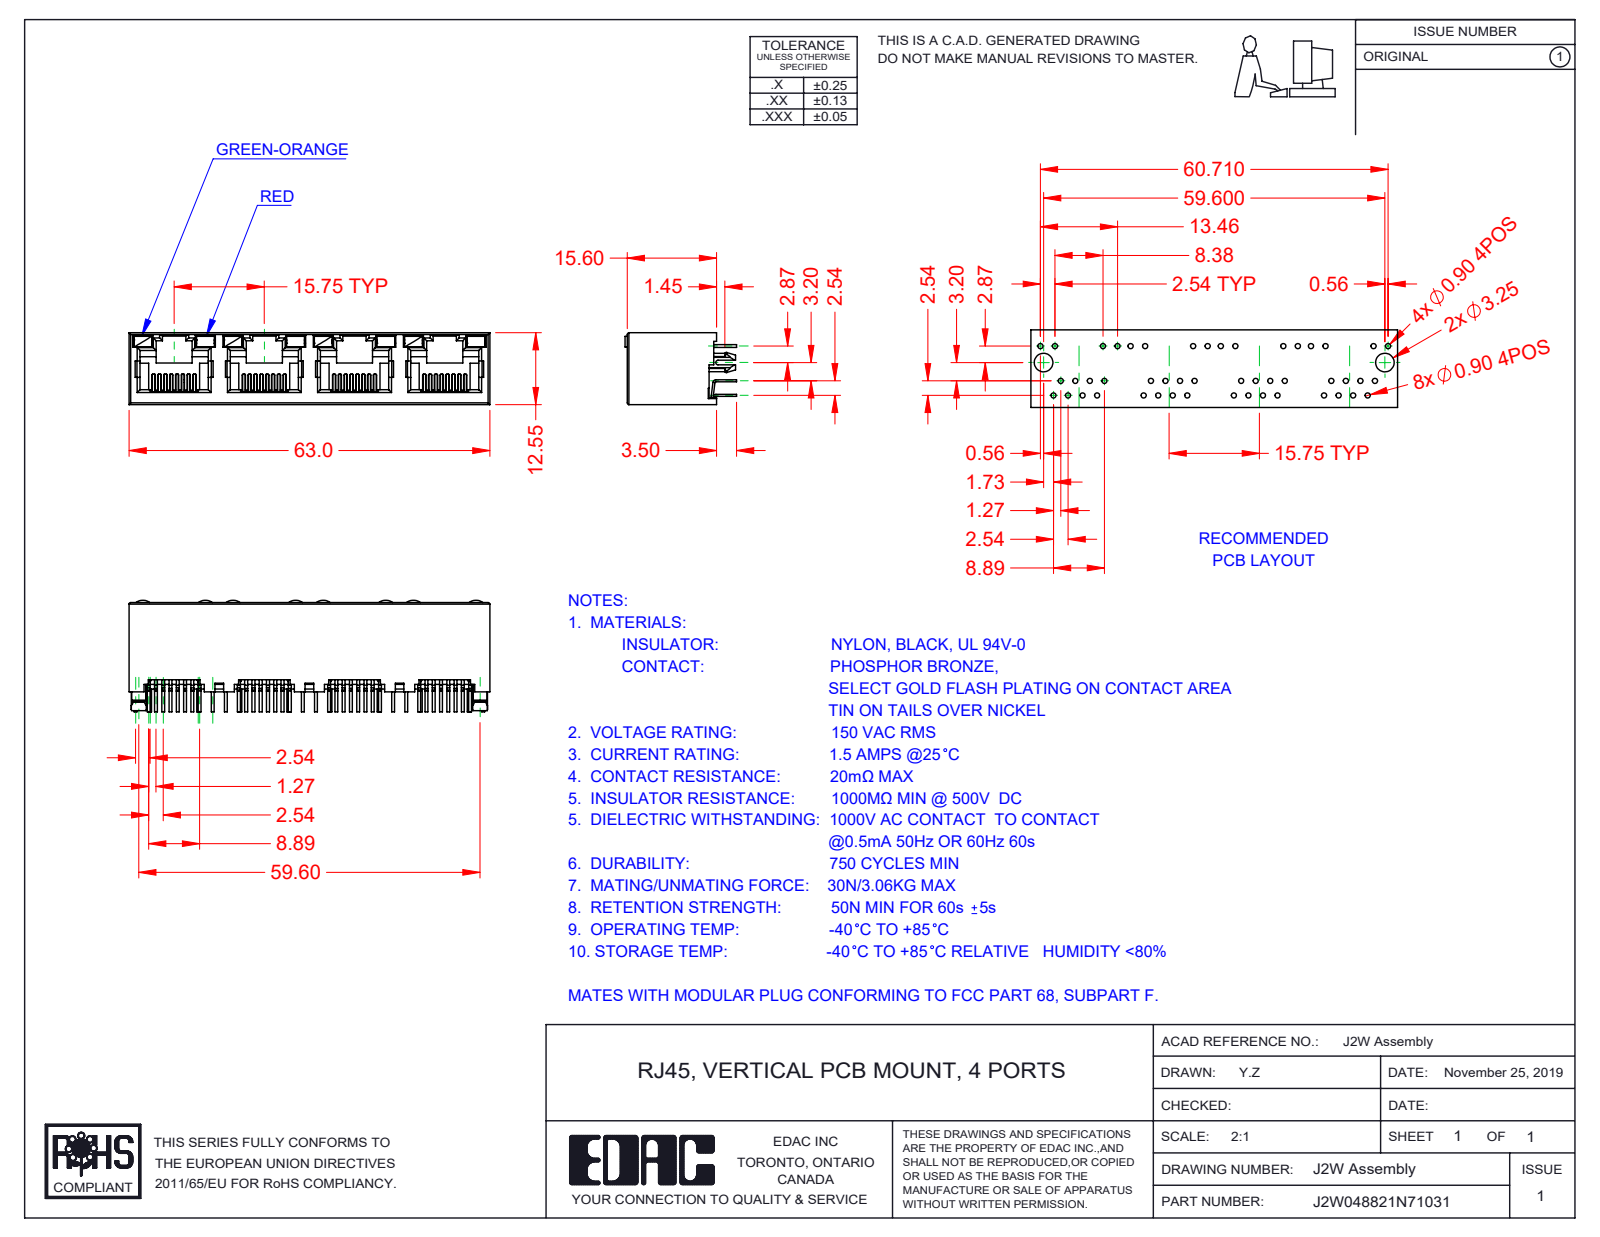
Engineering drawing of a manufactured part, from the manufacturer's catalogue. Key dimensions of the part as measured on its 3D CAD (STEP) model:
Part name (STEP PRODUCT): 2W LED RH_2-Red; 2W LED LH_7-Green-Orange; J2W048821N72131; 2W Contacts (+2 more)
STEP written by: SolidWorks 2016 (CONFIG_CONTROL_DESIGN)
Units: millimetres
Bodies: 45 solids, 3139 faces (2600 planar, 481 cylindrical, 58 other)
Overall size (bounding box): 63 × 19.5 × 12.55
Volume: 5 335 mm³ · Surface area: 13 144 mm²
Partial cylindrical surfaces — rounded edges, fillets, slot ends (radius × count): R0.15 ×64, R0.2 ×29, R0.5 ×28, R0.3 ×14, R0.45 ×8, R2 ×8, R0.25 ×2, R1.5 ×2
Main face-to-face distances: 12.55, 11.9, 0.65, 15.75, 0.36, 1.5, 0.78, 0.6, 11.3, 31.5
